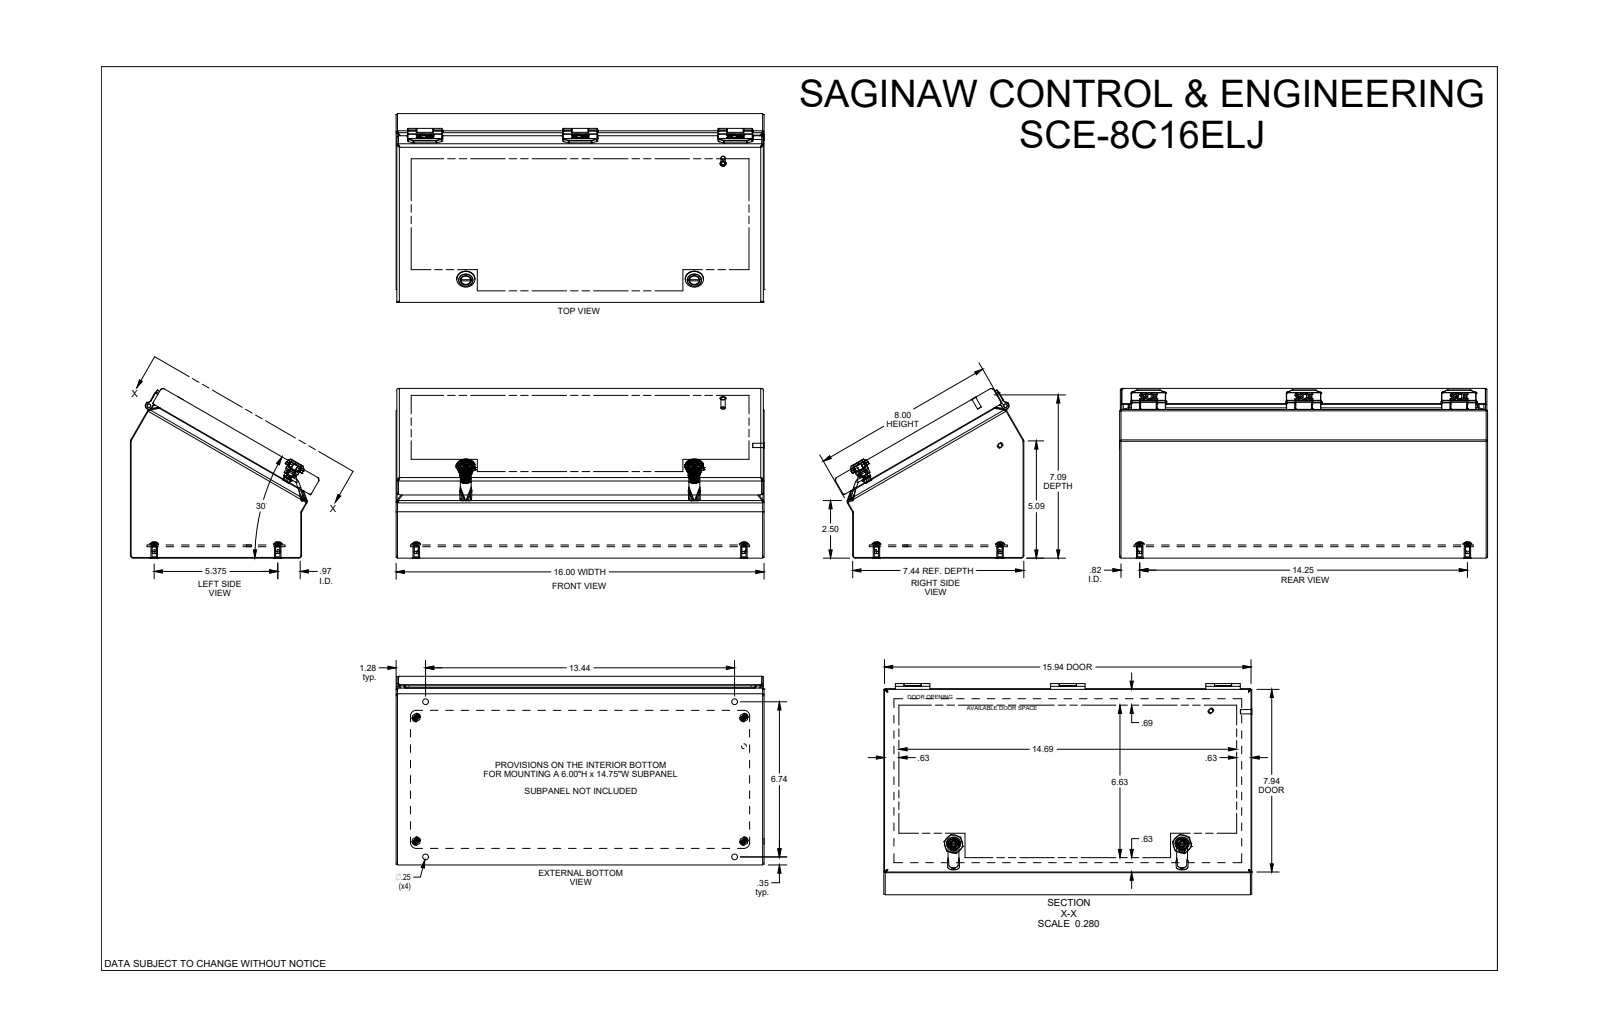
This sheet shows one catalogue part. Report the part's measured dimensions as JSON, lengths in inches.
{"part_name": "SCE-8C16ELJ", "step_written_by": "SolidWorks 2019 (AUTOMOTIVE_DESIGN)", "units": "inches", "bodies": {"solids": 33, "faces": 1460, "planar": 584, "cylindrical": 604, "other": 272}, "overall_size": [16.004, 8.201, 7.38], "volume_in3": 43.41, "surface_area_in2": 1354, "round_holes": [[0.25, 8], [0.19, 4], [0.281, 4], [0.02, 3], [0.1, 3], [0.174, 3], [0.266, 3], [0.193, 2], [0.2, 2], [0.239, 2], [0.254, 2], [0.269, 2]], "round_bosses_or_shafts": [[0.28, 4], [0.26, 3], [0.18, 3], [0.788, 2], [0.548, 2], [0.46, 2], [0.43, 2], [0.35, 2]], "partial_cylinders_radius": [[0.008, 48], [0.03, 36], [0.013, 31], [0.06, 24], [0.01, 22], [0.015, 22], [0.12, 16], [0.02, 13]], "face_to_face_distances": [0.06, 0.06, 0.436, 0.496, 0.075, 0.511, 0.571, 15.94, 7.382, 15.88], "hole_center_spacings": [0.795, 6.072, 6.75, 9.94, 13.861, 15.111, 5.375, 5.92]}
